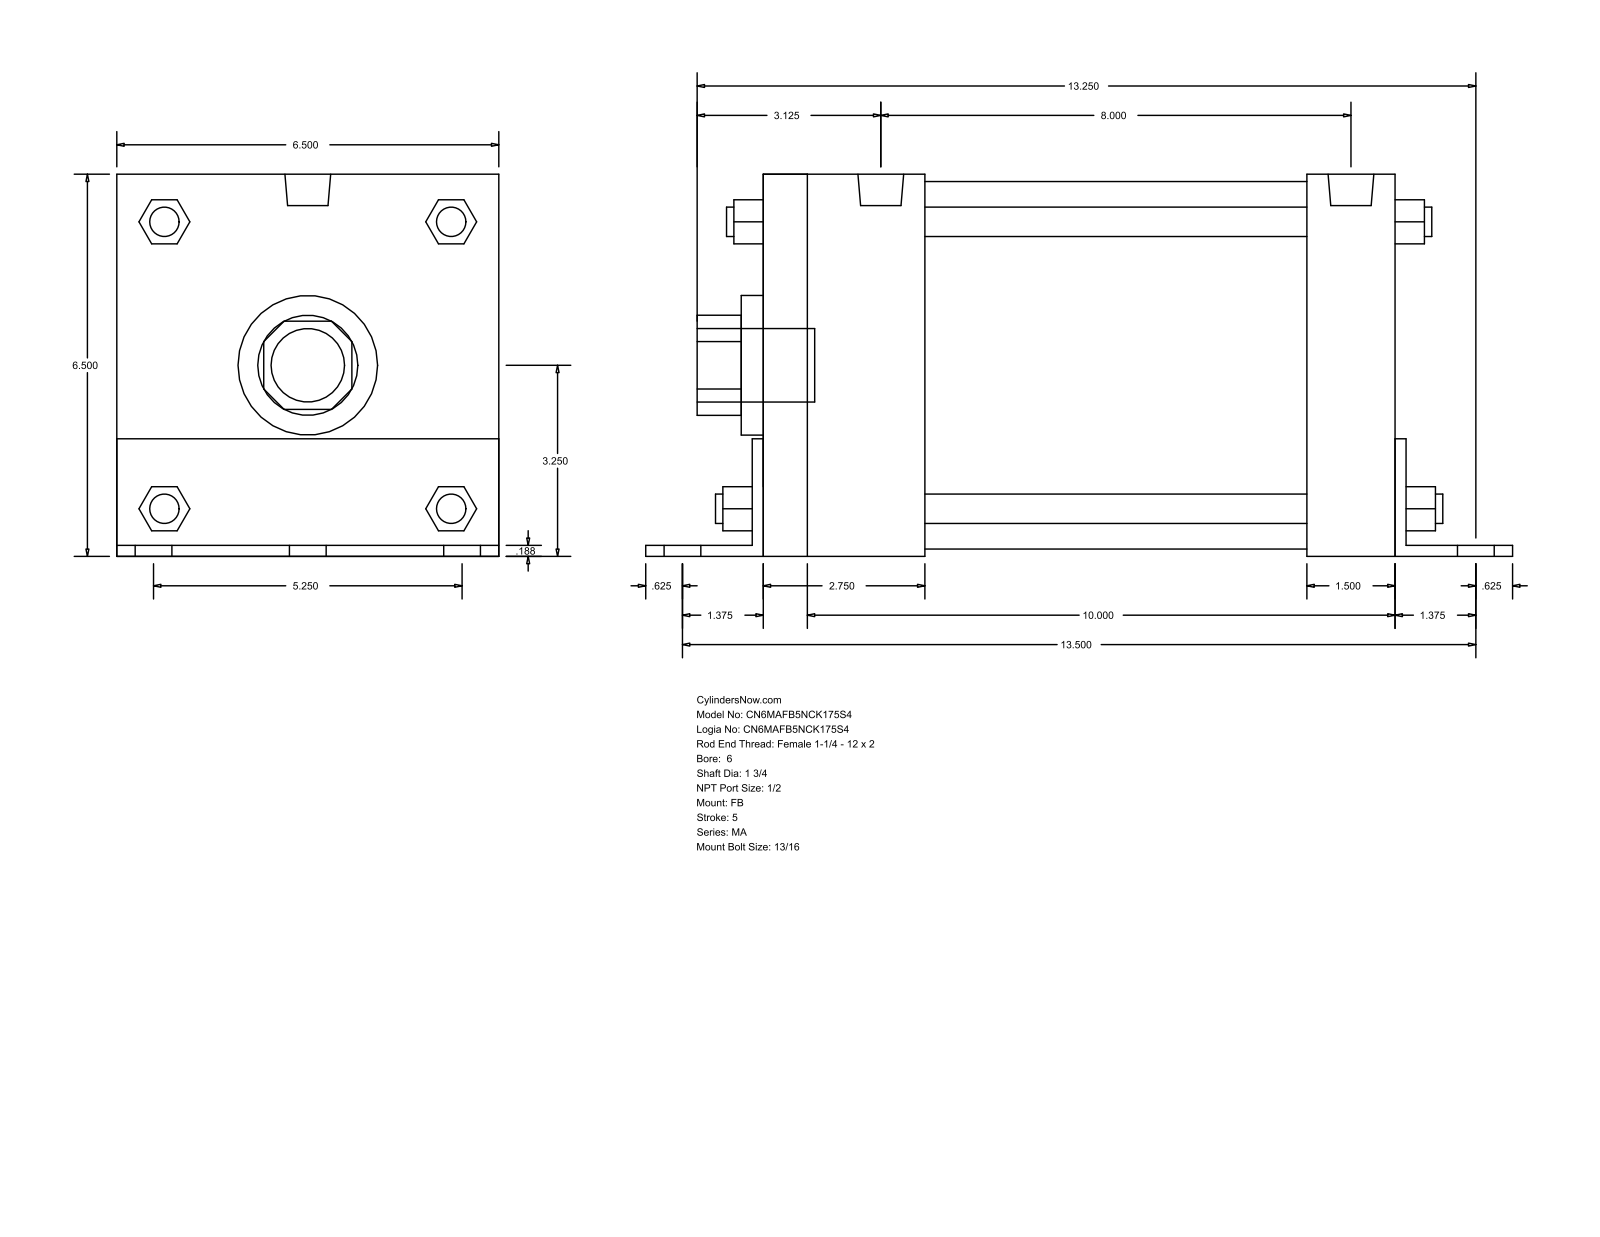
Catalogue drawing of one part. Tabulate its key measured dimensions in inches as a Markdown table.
| quantity | value |
| --- | --- |
| part name | MA_FB__0600_1.75 |
| STEP written by | GSSL Pune (CONFIG_CONTROL_DESIGN) |
| units | inches |
| bodies | 0 solids, 140 faces (105 planar, 35 cylindrical, 0 other) |
| overall size | 14.75 × 6.502 × 6.5 |
| round holes (diameter × count) | 1.75 × 1, 2.375 × 1, 6.25 × 1 |
| round bosses / shafts (diameter × count) | 0.813 × 6, 0.687 × 4, 0.5 × 4, 0.778 × 2, 1.25 × 1 |
| partial cylindrical surfaces (radius × count) | 0.852 × 1, 1.262 × 1 |
| main face-to-face distances | 6.5, 0.187, 10.75, 6.502, 0.185, 6.315, 1.5, 0.188, 10.938, 10.937 |
